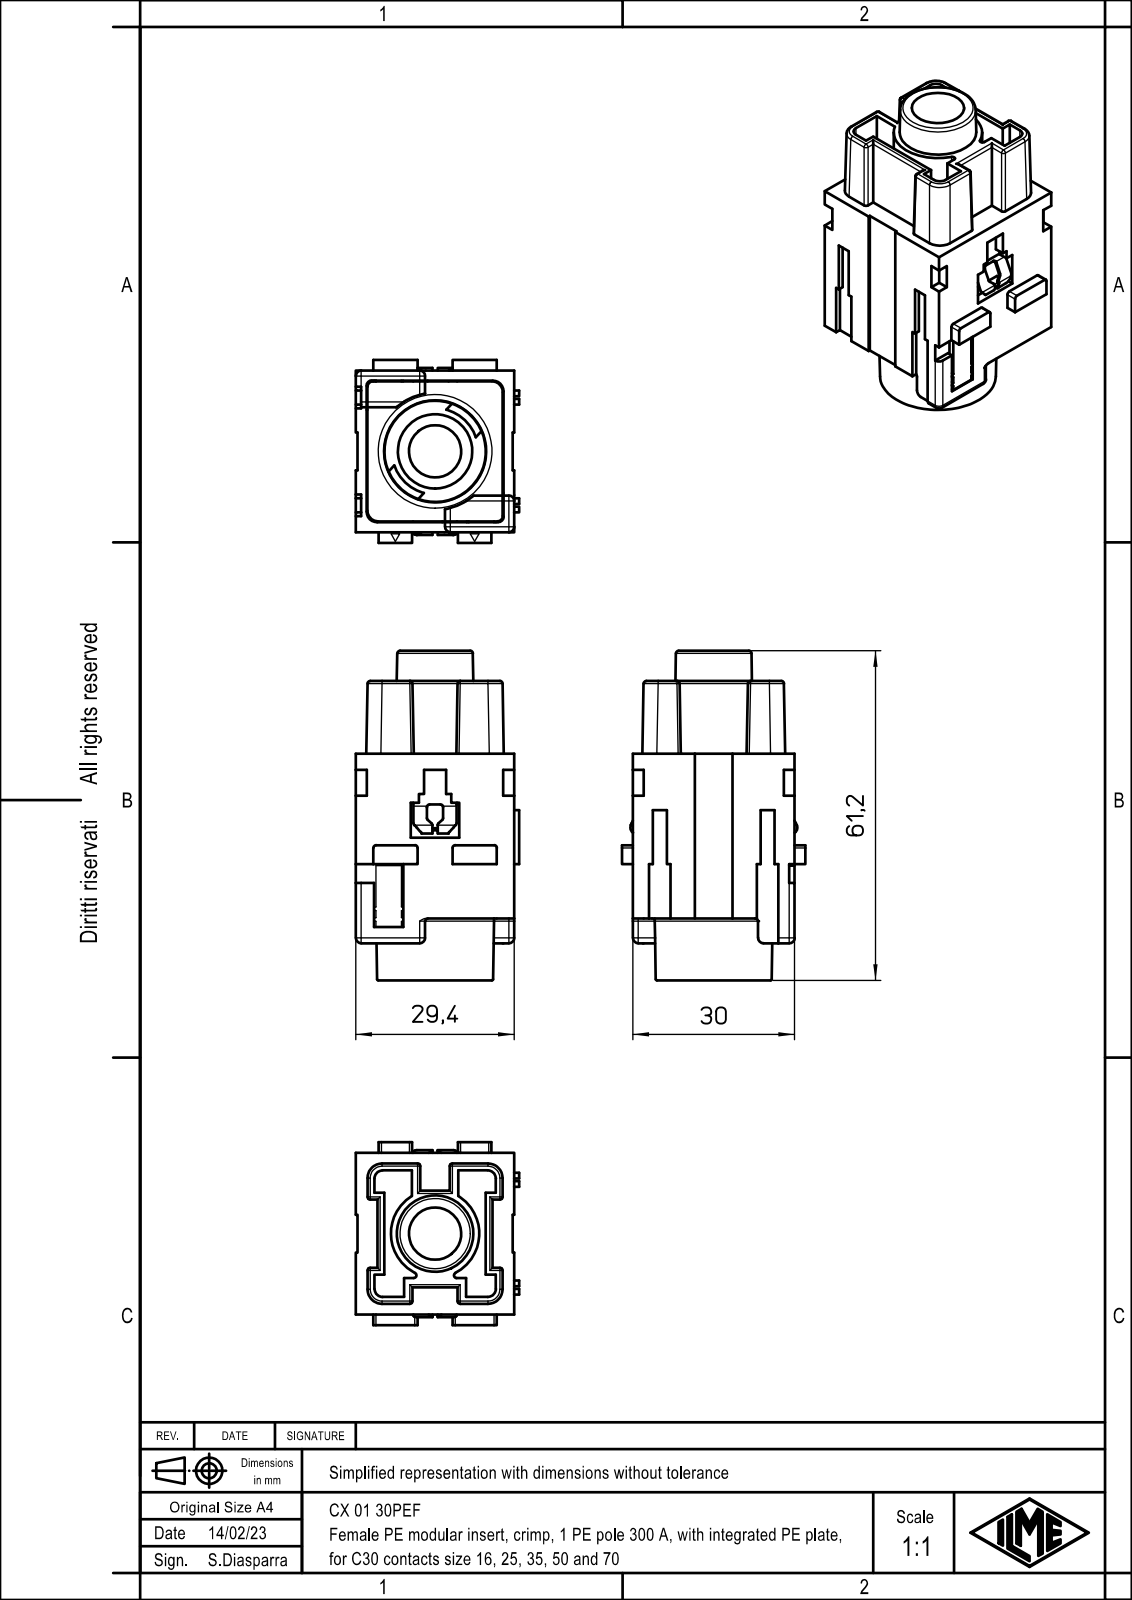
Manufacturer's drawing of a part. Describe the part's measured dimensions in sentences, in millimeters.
The part is named "CX 01 30PEF". Its 3-D file was written by "Creo Elements/Direct Modeling 20.1B 02-Apr-2019 (C) Parametric Technology GmbH (AUTOMOTIVE_DESIGN)". It is 1 solid with 470 faces: 267 planar, 133 cylindrical and 70 other. Overall it measures 61.2 by 34 by 30.3 millimeters. Its volume is 24 123 cubic millimeters and its surface area 19 085 square millimeters. Round holes: 1 of diameter 9.7, 1 of diameter 13.8, 1 of diameter 18.8. Partial cylindrical surfaces (rounded edges, fillets, slot ends): 54 of radius 0.5, 17 of radius 1, 8 of radius 0.35, 4 of radius 0.8, 4 of radius 1.1, 4 of radius 1.5, 4 of radius 2.7, 2 of radius 2. The main face-to-face distances are 2, 1.85, 25.25, 28, 27.4, 2.15, 27.25, 28.15, 26.15, 30.
